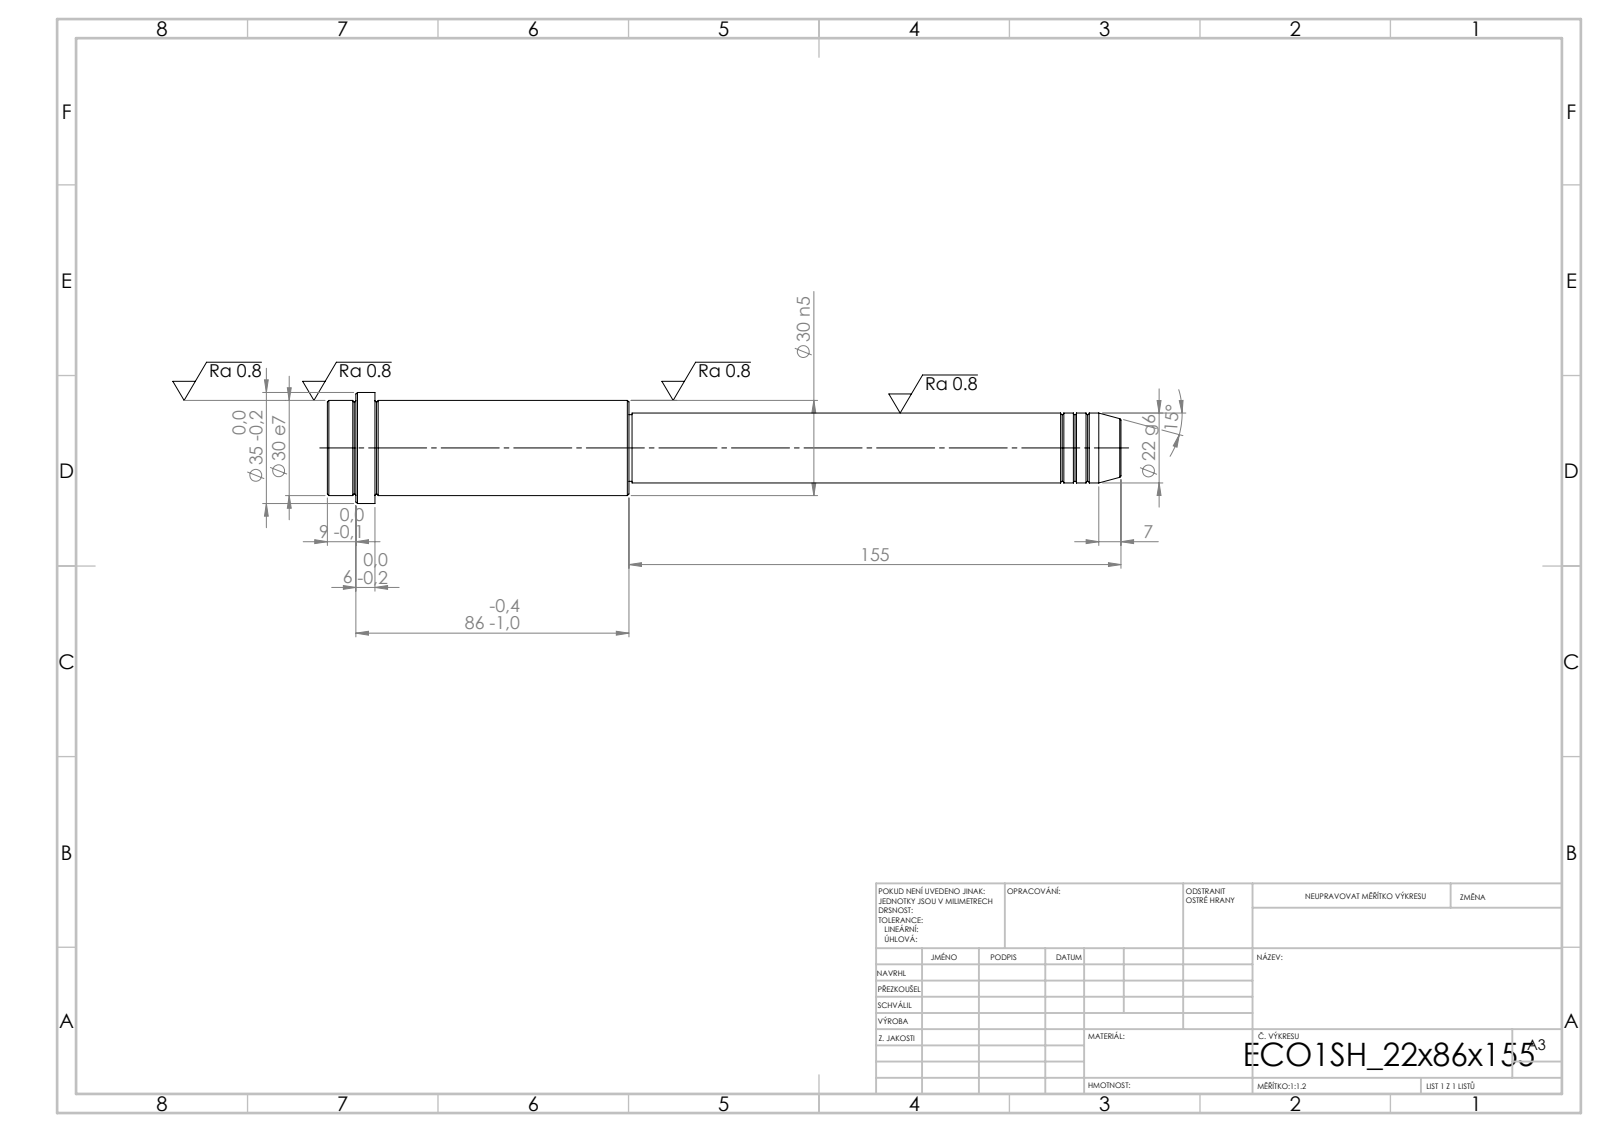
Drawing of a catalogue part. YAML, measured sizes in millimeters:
step_written_by: "SolidWorks 2019 (CONFIG_CONTROL_DESIGN)"
units: millimeters
bodies: {solids: 1, faces: 52, planar: 6, cylindrical: 16, other: 30}
overall_size: [250, 35, 35]
volume: 126951
surface_area: 21720
round_bosses_or_shafts:
  - {diameter: 35, count: 1}
  - {diameter: 30, count: 1}
  - {diameter: 22, count: 1}
  - {diameter: 21, count: 1}
face_to_face_distances: [95, 80, 15, 155, 235, 250, 241, 86, 6, 9]
